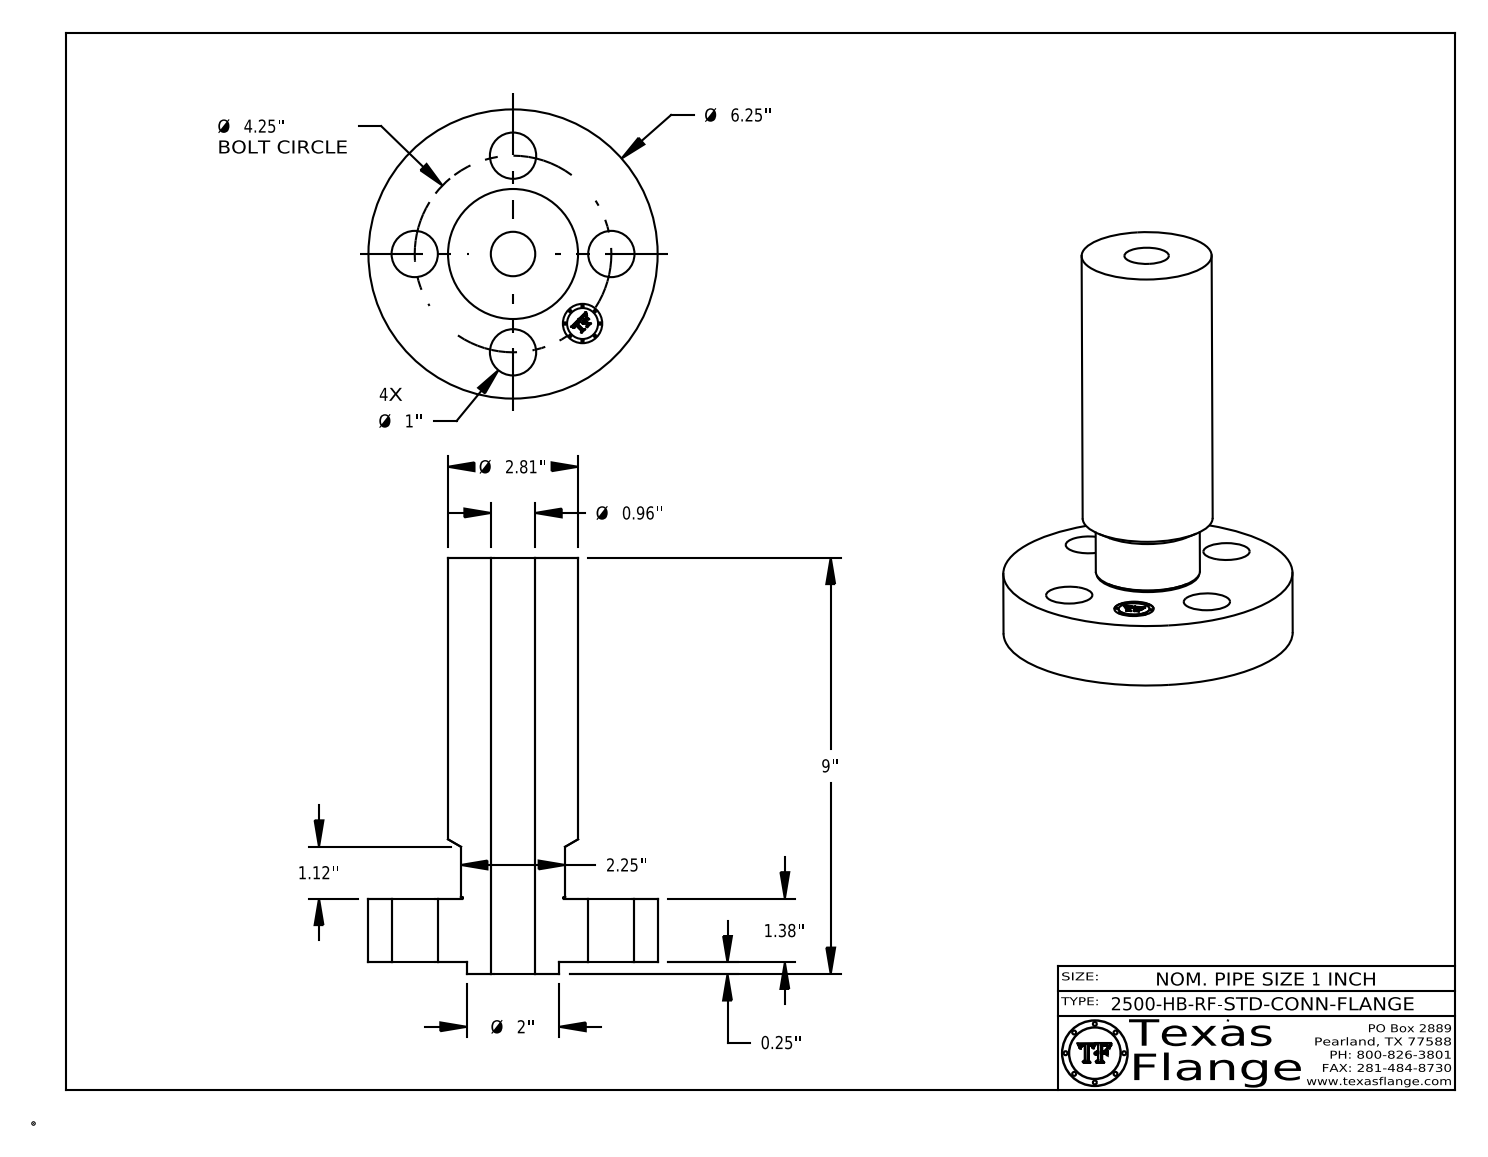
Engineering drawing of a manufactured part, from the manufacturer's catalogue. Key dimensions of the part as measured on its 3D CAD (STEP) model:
Part name (STEP PRODUCT): 1-2500-HB-RF-STD-CONN-FLANGE
STEP written by: CATIA V5 STEP AP214 (AUTOMOTIVE_DESIGN)
Units: inches
Bodies: 1 solid, 413 faces (369 planar, 38 cylindrical, 6 other)
Overall size (bounding box): 9 × 6.25 × 6.25
Volume: 75.29 in³ · Surface area: 193.6 in²
Round holes (diameter × count): ⌀1 ×4, ⌀0.85 ×1, ⌀0.96 ×1
Round bosses / shafts (diameter × count): ⌀0.051 ×8, ⌀6.25 ×1, ⌀2.81 ×1, ⌀2.25 ×1, ⌀2 ×1, ⌀0.67 ×1
Main face-to-face distances: 1.38, 8.75, 7.37, 0.25, 1.63, 9, 1.625, 1.375, 7.375, 0.254
Hole centre spacings: 2.125, 3.006, 1.626, 3.927, 4.25
